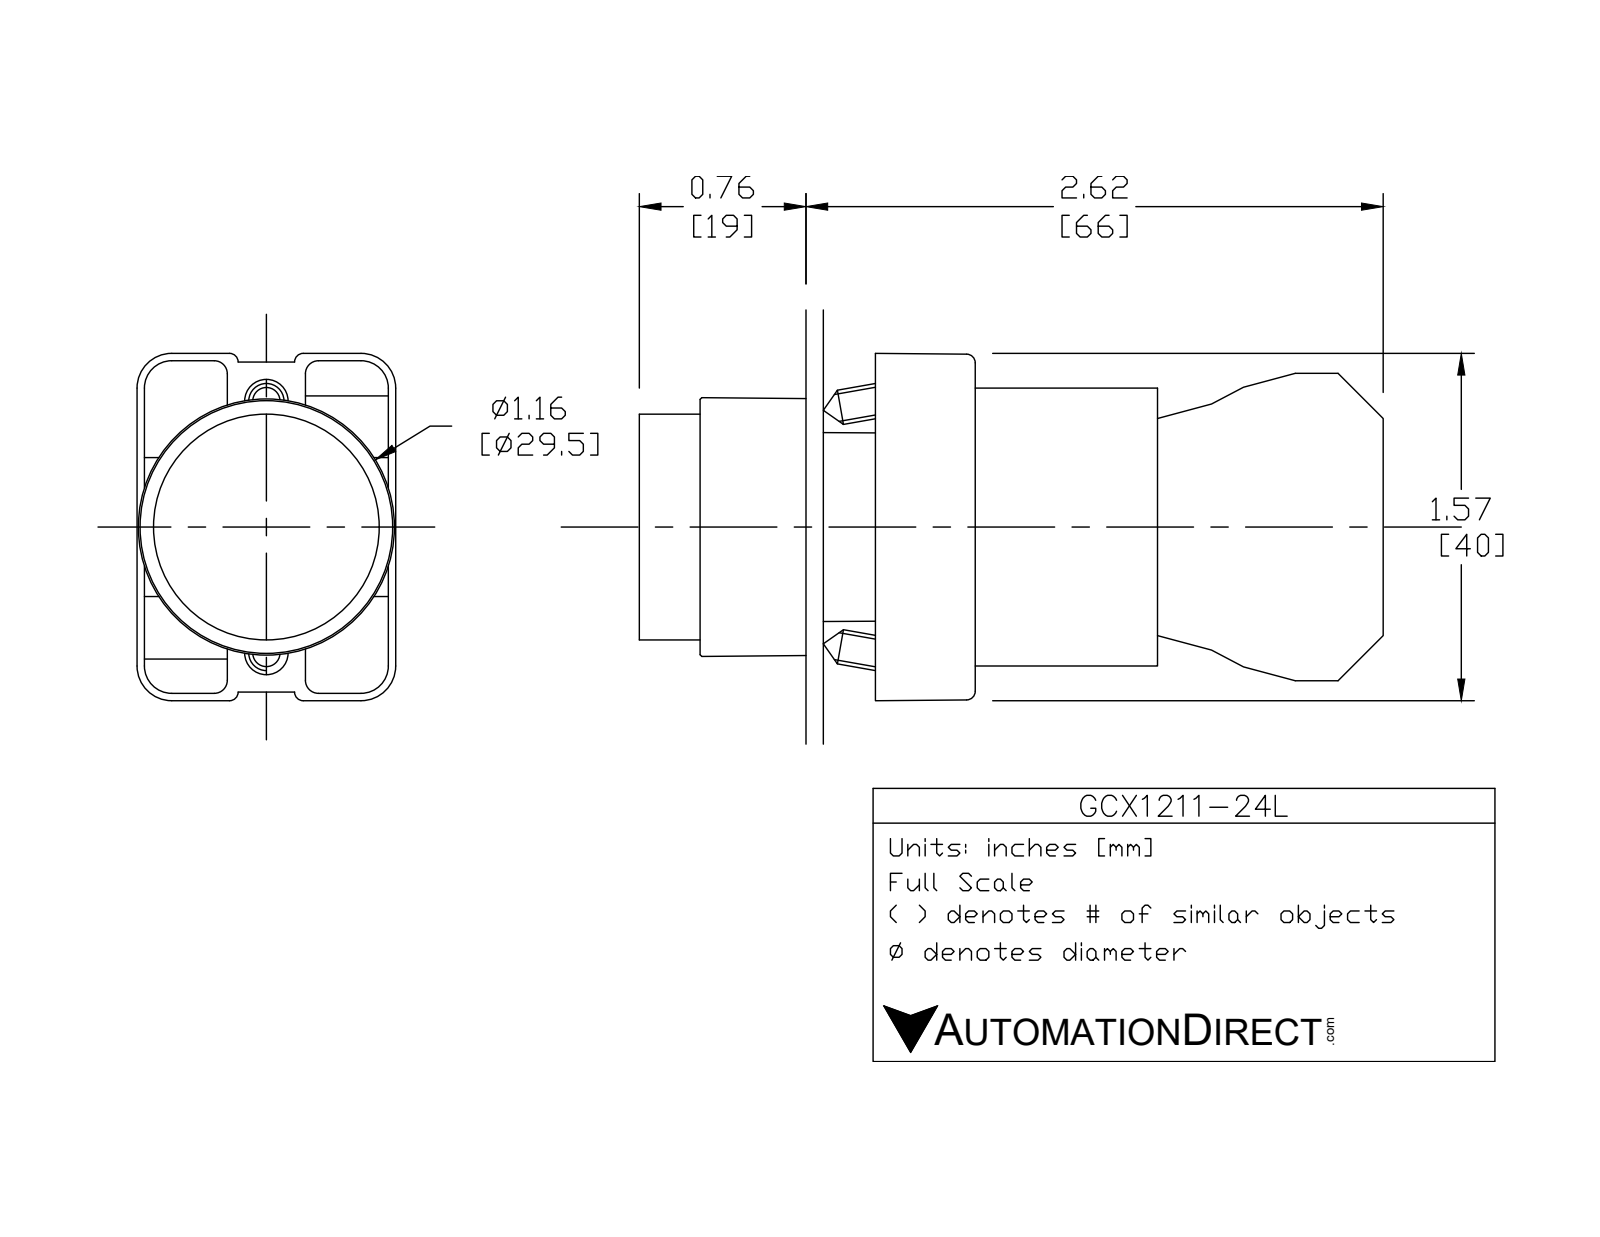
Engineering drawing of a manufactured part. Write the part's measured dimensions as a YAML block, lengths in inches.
part_name: "GCX1211-24L; ECX1050; GCX1211L OPERATOR; ecx1030 (+1 more)"
step_written_by: "SolidWorks 2016 (AUTOMOTIVE_DESIGN)"
units: inches
bodies: {solids: 7, faces: 425, planar: 250, cylindrical: 144, other: 31}
overall_size: [3.319, 1.581, 1.177]
volume: 2.721
surface_area: 36.32
round_holes:
  - {diameter: 0.079, count: 2}
  - {diameter: 0.124, count: 2}
  - {diameter: 0.13, count: 2}
  - {diameter: 0.087, count: 1}
  - {diameter: 0.197, count: 1}
  - {diameter: 0.469, count: 1}
  - {diameter: 0.878, count: 1}
  - {diameter: 0.888, count: 1}
  - {diameter: 1.024, count: 1}
round_bosses_or_shafts:
  - {diameter: 0.157, count: 4}
  - {diameter: 1.175, count: 1}
  - {diameter: 1.004, count: 1}
  - {diameter: 0.945, count: 1}
  - {diameter: 0.856, count: 1}
  - {diameter: 0.78, count: 1}
  - {diameter: 0.504, count: 1}
partial_cylinders:
  - {radius: 0.059, count: 24}
  - {radius: 0.041, count: 12}
  - {radius: 0.124, count: 12}
  - {radius: 0.157, count: 12}
  - {radius: 0.039, count: 8}
  - {radius: 0.128, count: 2}
  - {radius: 0.02, count: 1}
  - {radius: 0.063, count: 1}
face_to_face_distances: [0.827, 0.579, 1.171, 2.02, 1.193, 0.031, 0.033, 0.573, 1.165, 0.593]
hole_center_spacings: [0.236, 0.544, 0.472, 0.49]
